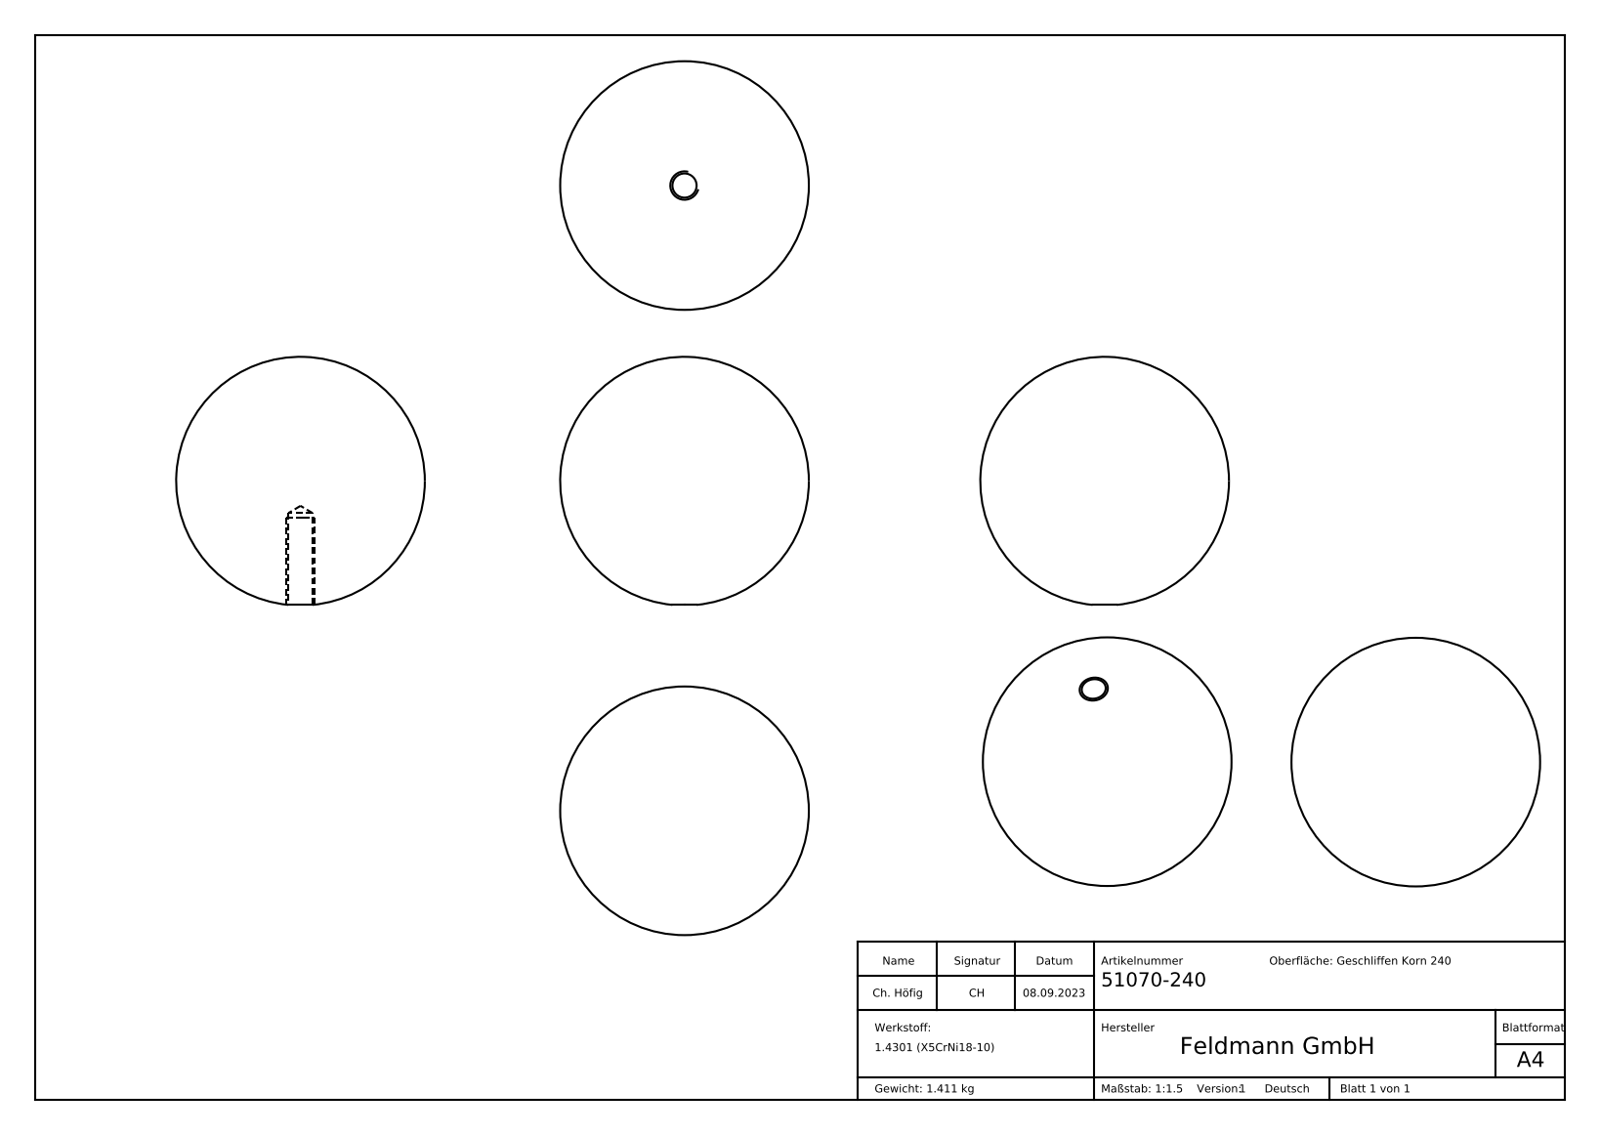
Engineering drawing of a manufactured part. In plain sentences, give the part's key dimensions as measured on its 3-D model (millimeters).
The part is named "51070-240". Its 3-D file was written by "SolidWorks 2018 (CONFIG_CONTROL_DESIGN)". It is 1 solid with 3 faces: 0 planar, 1 cylindrical and 2 other. Overall it measures 70 by 70 by 69.83 millimeters. Its volume is 178 628 cubic millimeters and its surface area 15 952 square millimeters. Round holes: 1 of diameter 6.8.
